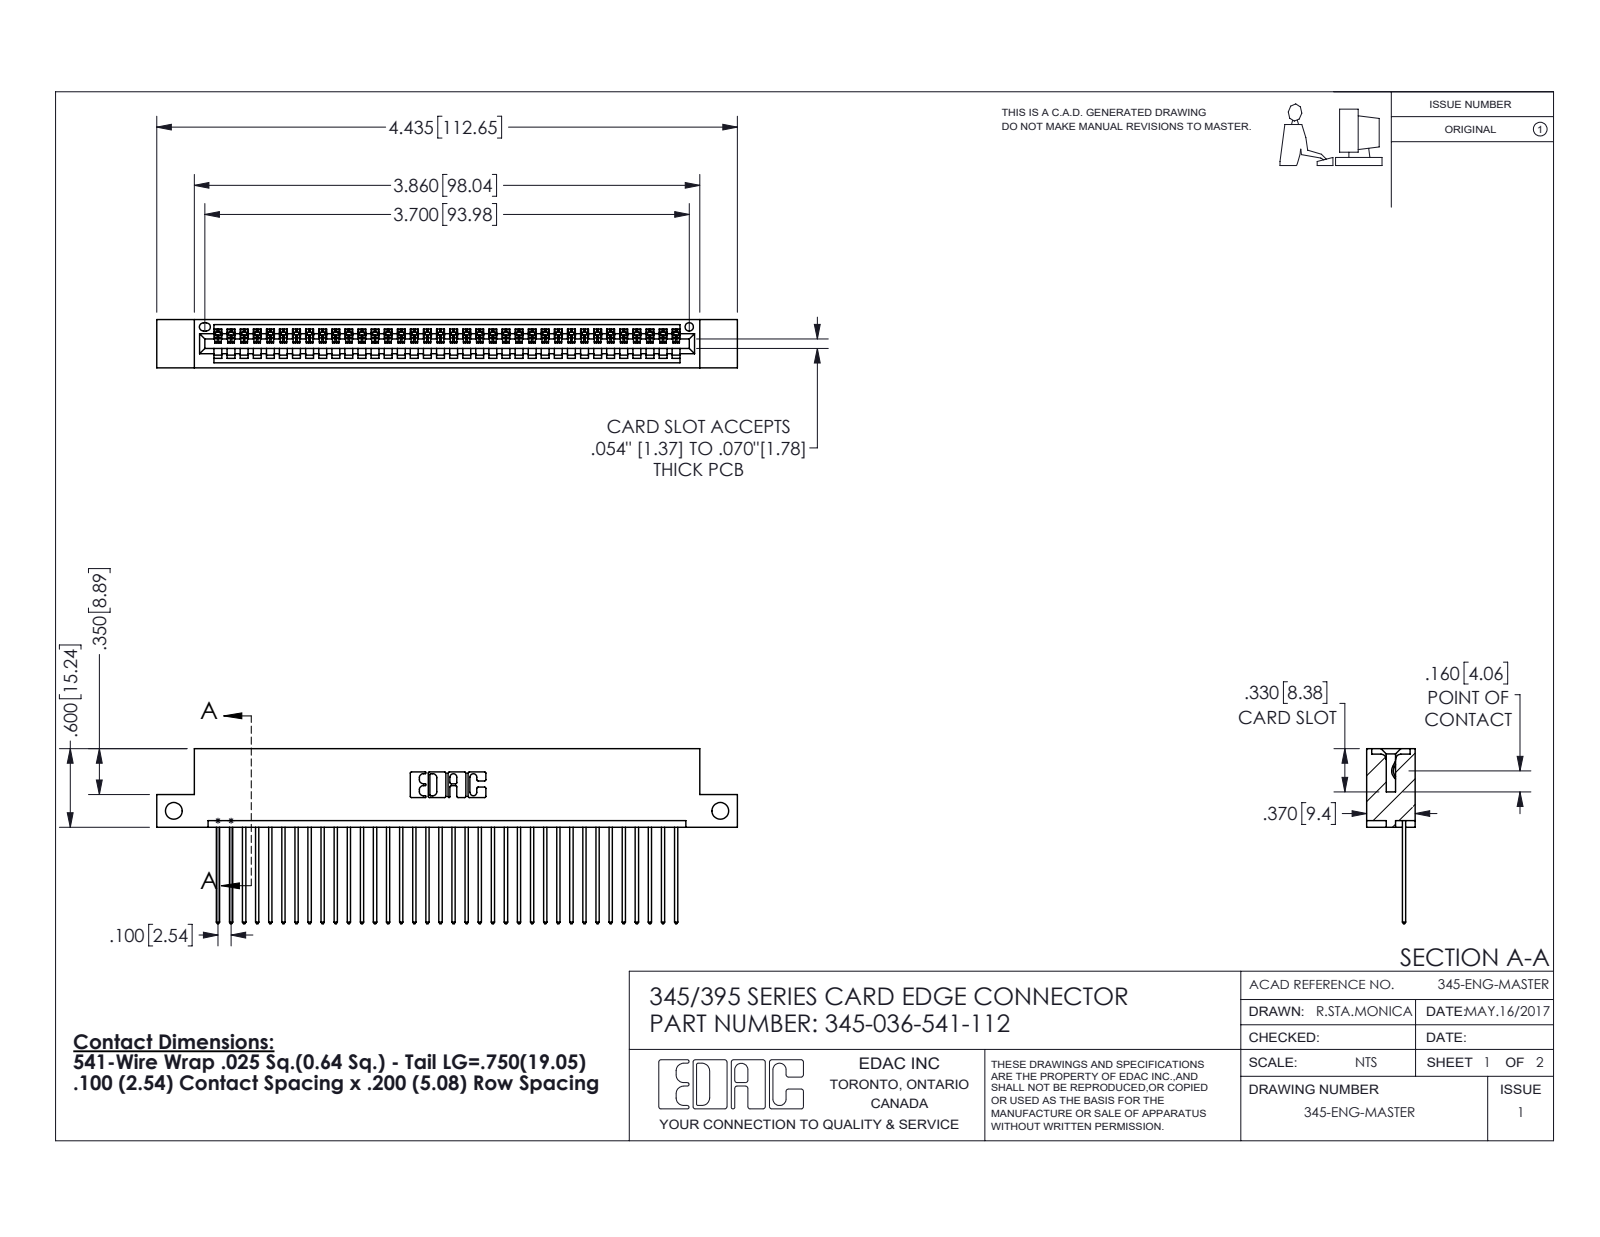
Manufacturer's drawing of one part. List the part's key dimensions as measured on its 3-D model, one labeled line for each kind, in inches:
Part name (STEP PRODUCT): 345-292-001_345-293-141; 345-036-541-112; 345 Part_Flush Mounting Lugs - Side Mount
STEP written by: SolidWorks 2016 (CONFIG_CONTROL_DESIGN)
Units: inches
Bodies: 37 solids, 2214 faces (1520 planar, 694 cylindrical, 0 other)
Overall size (bounding box): 4.435 × 1.337 × 0.37
Volume: 0.652 in³ · Surface area: 22.74 in²
Round holes (diameter × count): ⌀0.128 ×2, ⌀0.064 ×1
Partial cylindrical surfaces — rounded edges, fillets, slot ends (radius × count): R0.006 ×72, R0.01 ×72, R0.01 ×22, R0.007 ×6, R0.031 ×6, R0.026 ×3, R0.031 ×2, R0.04 ×2
Main face-to-face distances: 0.072, 0.298, 0.098, 0.272, 0.025, 0.37, 0.2, 0.225, 0.149, 0.072
Hole centre spacings: 4.175
